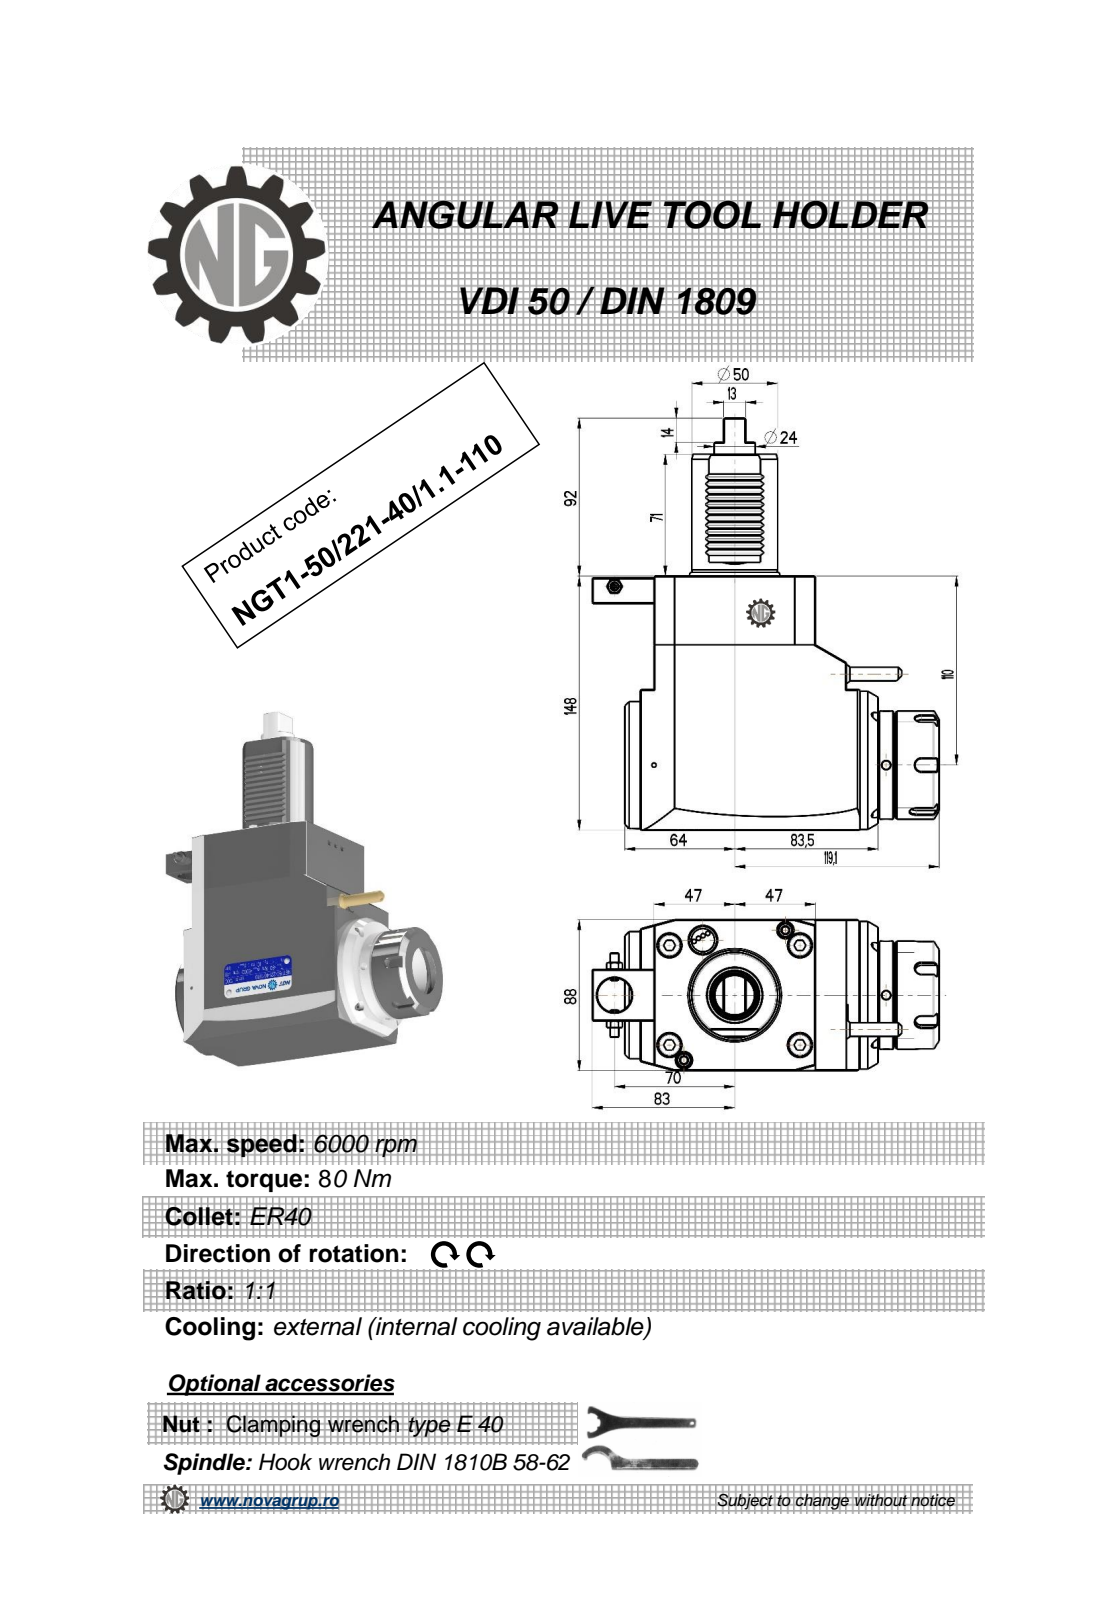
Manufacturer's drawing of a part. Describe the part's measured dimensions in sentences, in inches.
The part is named "NGT1_50_221_40_1_1_110". Its 3-D file was written by "PRO/ENGINEER BY PARAMETRIC TECHNOLOGY CORPORATION, 2010280 (CONFIG_CONTROL_DESIGN)". It is 1 solid with 411 faces: 206 planar, 91 cylindrical and 114 other. Overall it measures 9.449 by 7.957 by 3.465 inches. Its volume is 111.8 cubic inches and its surface area 177.6 square inches. Round holes: 3 of diameter 0.197, 1 of diameter 0.118, 1 of diameter 0.374, 1 of diameter 0.787, 1 of diameter 1.319. Round bosses or shafts: 1 of diameter 3.386, 1 of diameter 2.913, 1 of diameter 2.48, 1 of diameter 2.008, 1 of diameter 1.969, 1 of diameter 0.945, 1 of diameter 0.394, 1 of diameter 0.353. Partial cylindrical surfaces (rounded edges, fillets, slot ends): 12 of radius 0.01, 12 of radius 0.012, 6 of radius 0.008, 5 of radius 0.148, 2 of radius 0.031, 1 of radius 0.098. The main face-to-face distances are 3.465, 5.827, 5.807, 0.669, 0.315, 3.701, 4.37, 0.354, 5.138, 1.437. The hole center spacings are 2.065, 2.23, 3.996, 6.23.
